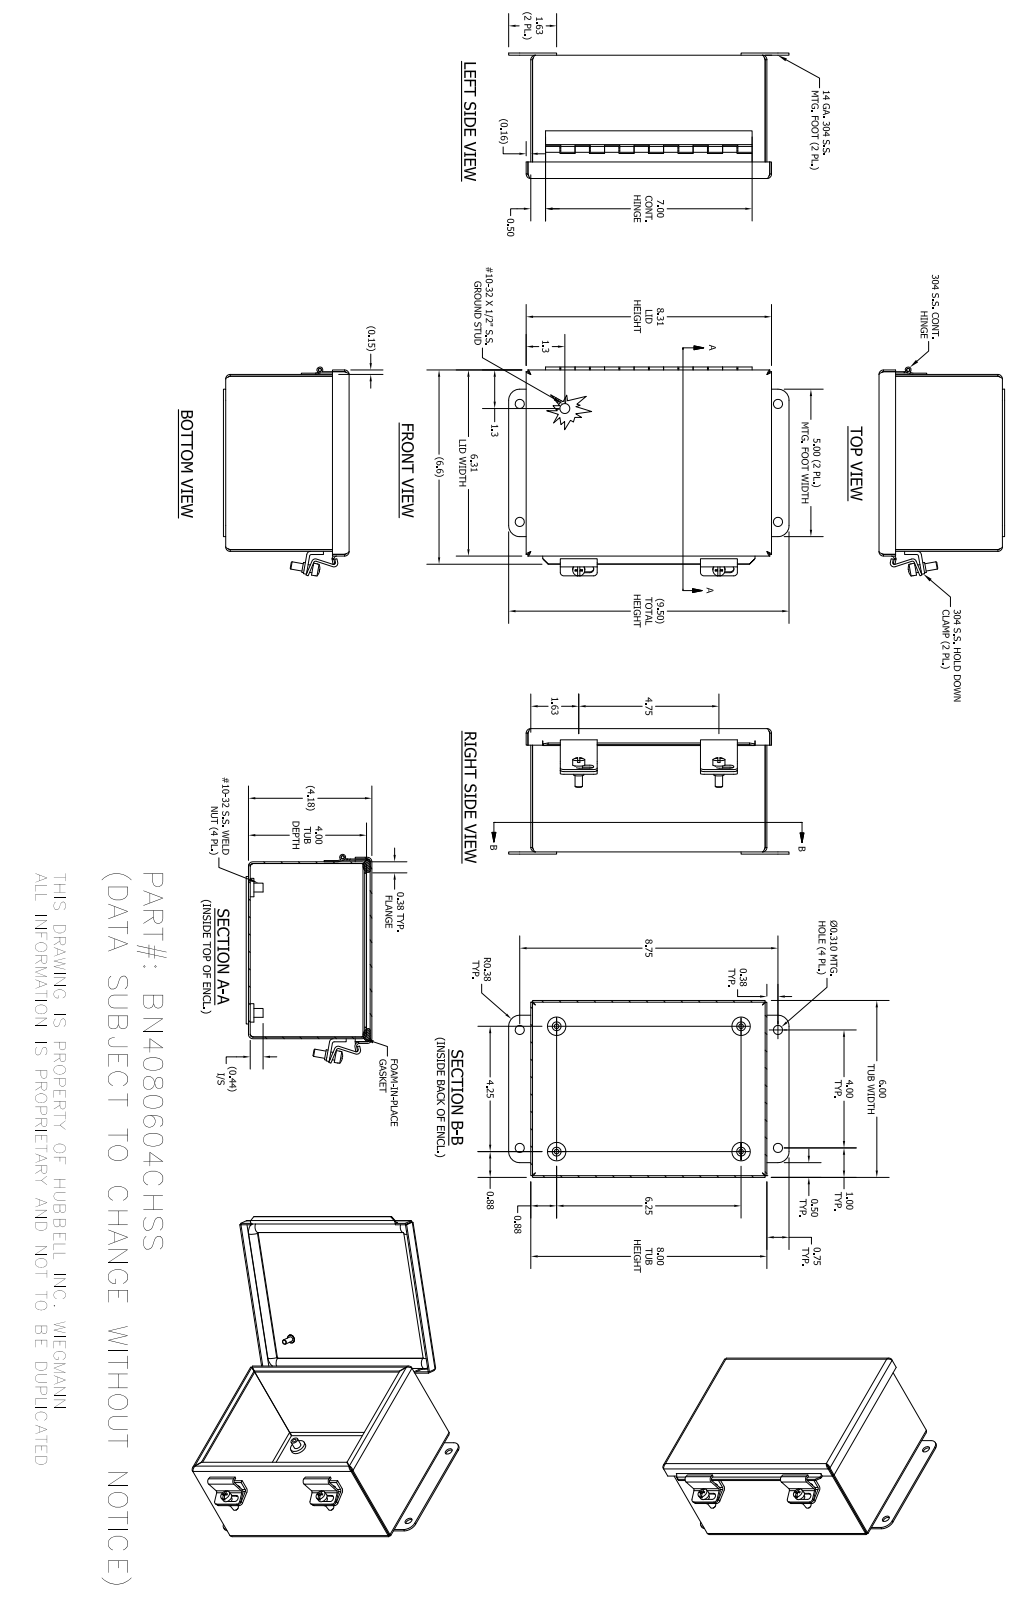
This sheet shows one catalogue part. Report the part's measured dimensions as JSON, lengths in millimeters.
{"part_name": "B_080604_SSBKP; H4050547LH; H4050547P; H4050547TH (+8 more)", "step_written_by": "Autodesk Inventor 2016 (AUTOMOTIVE_DESIGN)", "units": "millimeters", "bodies": {"solids": 19, "faces": 428, "planar": 232, "cylindrical": 129, "other": 67}, "overall_size": [241.3, 179.98, 108.11], "volume_mm3": 302225, "surface_area_mm2": 373638, "round_holes": [[2.79, 4], [3.96, 4], [7.87, 4], [4.98, 2], [2.96, 1]], "round_bosses_or_shafts": [[15.88, 4], [7.62, 4], [10.4, 2], [8.74, 2], [6.35, 2], [8.56, 1], [5.08, 1], [4.83, 1]], "partial_cylinders_radius": [[2.38, 13], [3.88, 13], [1.68, 8], [3.17, 8], [3.38, 4], [5.78, 4], [9.53, 4], [1.6, 3]], "face_to_face_distances": [1.5, 104.71, 150.9, 106.21, 103.21, 201.7, 152.4, 149.4, 203.2, 200.2], "hole_center_spacings": [101.6, 109.48, 120.65, 217.41, 19.05, 31.9, 31.91, 107.95]}
